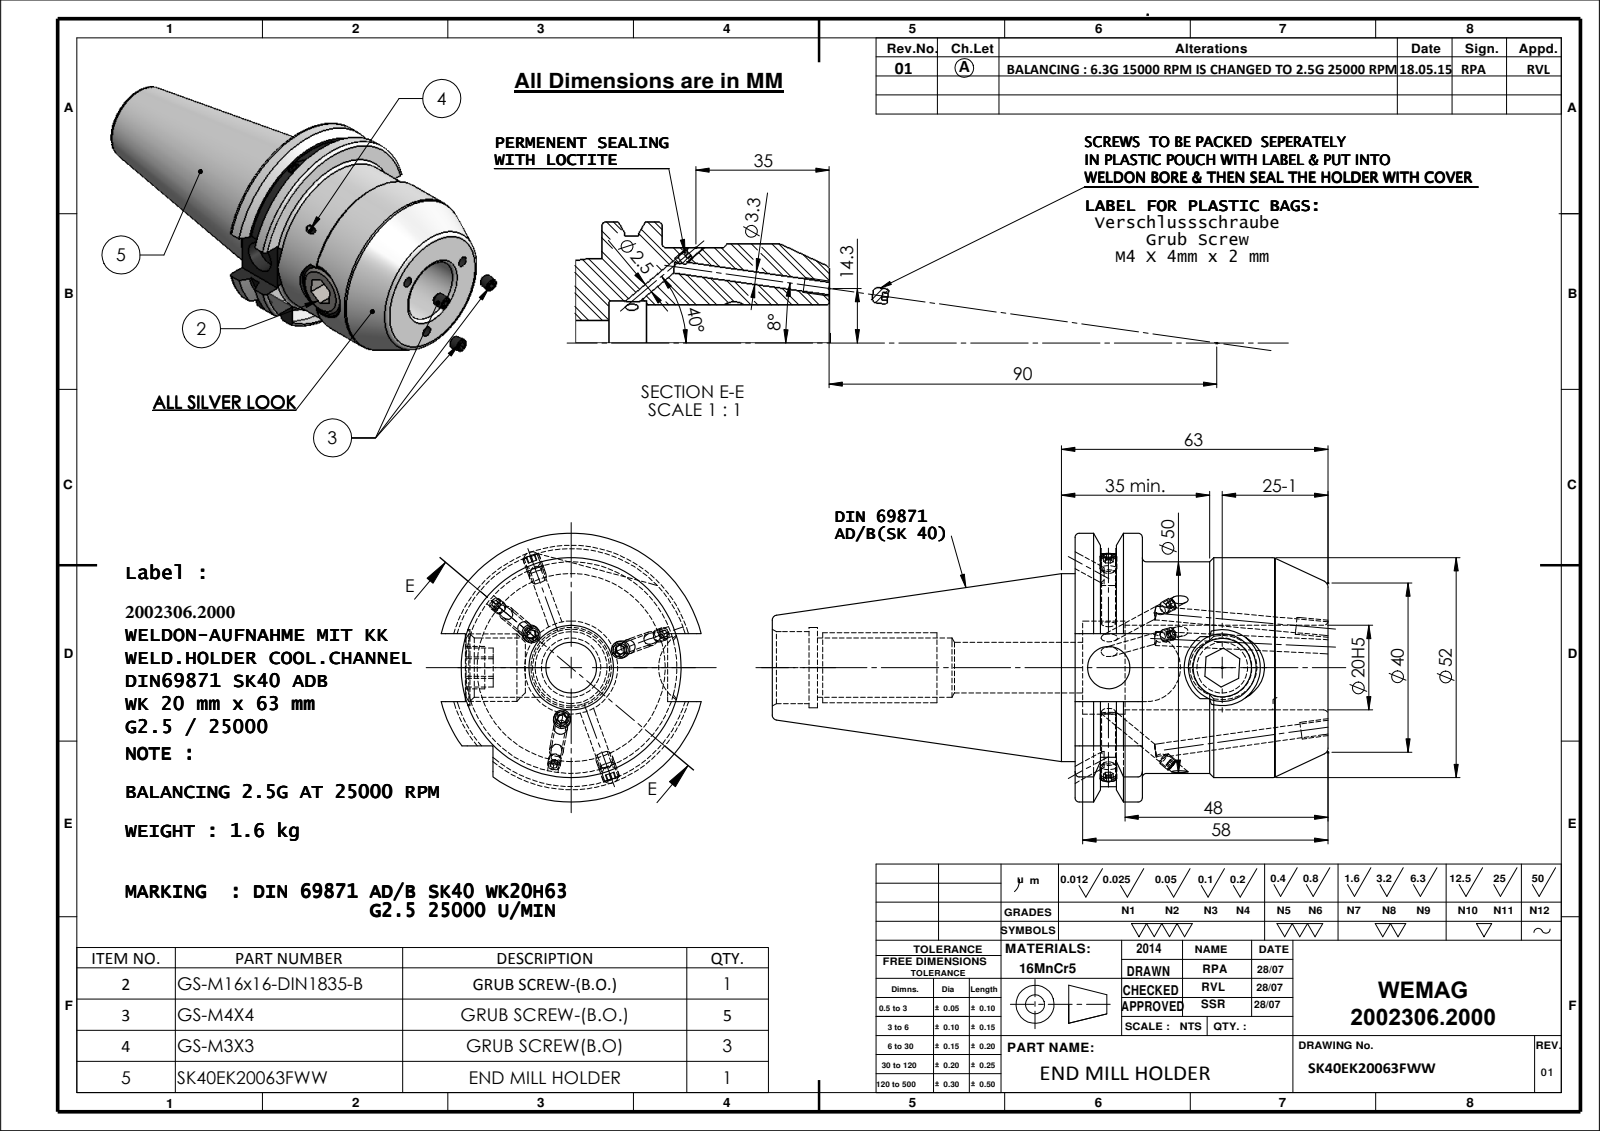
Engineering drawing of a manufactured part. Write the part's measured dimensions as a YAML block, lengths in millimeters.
part_name: "Copy of M4X4_DIN 913 - M4 x 4-N; SK40 EK 20 063 FTC WW.; M16X16_ISO 4026 - M16 x 10-N"
step_written_by: "SolidWorks 2009 (CONFIG_CONTROL_DESIGN)"
units: millimeters
bodies: {solids: 6, faces: 201, planar: 78, cylindrical: 53, other: 70}
overall_size: [147.15, 63.55, 61.48]
volume: 166451
surface_area: 33452
round_holes:
  - {diameter: 3.3, count: 3}
  - {diameter: 14, count: 2}
  - {diameter: 10, count: 1}
  - {diameter: 12, count: 1}
  - {diameter: 17, count: 1}
  - {diameter: 19, count: 1}
  - {diameter: 20, count: 1}
  - {diameter: 22, count: 1}
round_bosses_or_shafts:
  - {diameter: 4, count: 4}
  - {diameter: 52, count: 1}
  - {diameter: 50, count: 1}
  - {diameter: 44.45, count: 1}
  - {diameter: 16, count: 1}
partial_cylinders:
  - {radius: 8.05, count: 1}
  - {radius: 28.12, count: 1}
  - {radius: 31.77, count: 1}
face_to_face_distances: [59.8, 15.9, 43.9, 1.8, 14.1, 58, 16.1, 47.8, 71.6, 73.4]
hole_center_spacings: [26.85]
